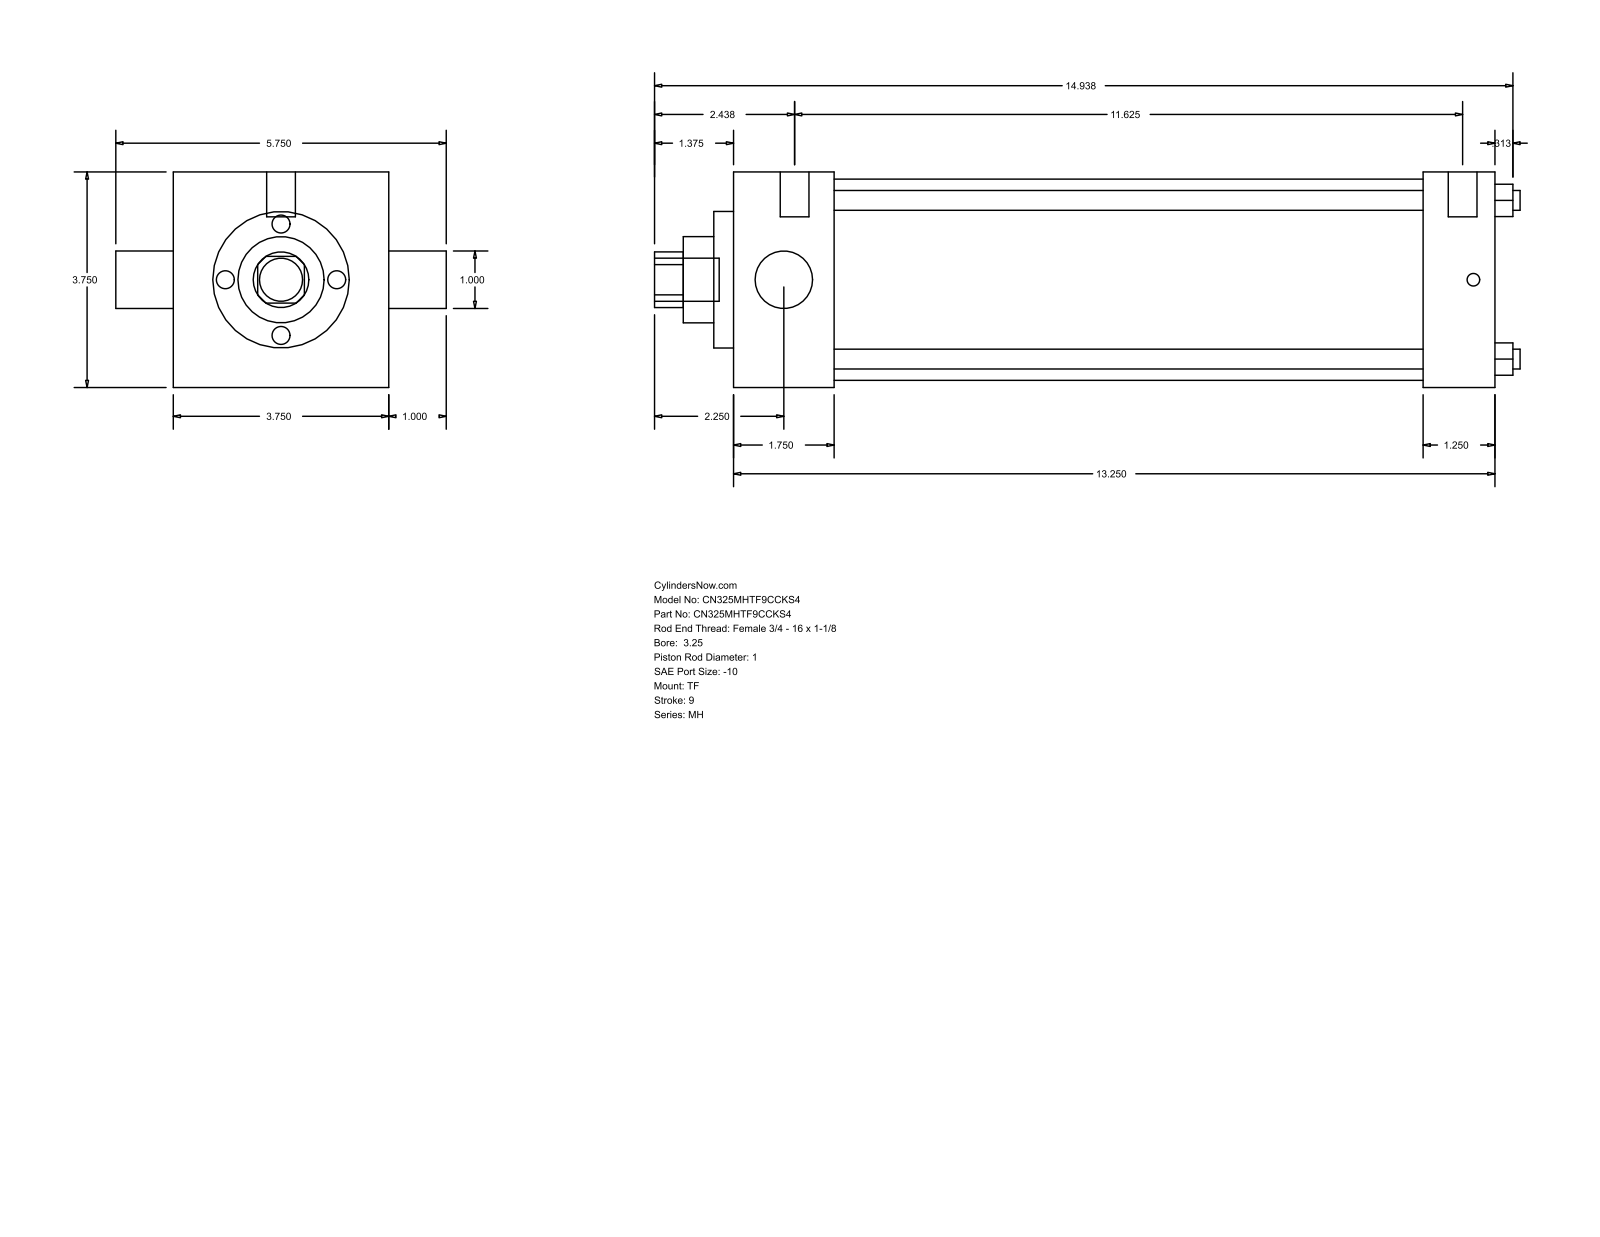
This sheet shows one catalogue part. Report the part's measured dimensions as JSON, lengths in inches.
{"part_name": "MH_TF__0325_1", "step_written_by": "GSSL Pune (CONFIG_CONTROL_DESIGN)", "units": "inches", "bodies": {"solids": 0, "faces": 86, "planar": 61, "cylindrical": 25, "other": 0}, "overall_size": [15.063, 5.75, 3.75], "round_holes": [[0.345, 4], [1, 2], [1.5, 1], [2.375, 1], [3.5, 1]], "round_bosses_or_shafts": [[0.219, 3], [0.5, 2], [0.75, 1]], "partial_cylinders_radius": [[0.484, 1]], "face_to_face_distances": [3.75, 13.25, 1.75, 12, 10.25, 11.5, 1.25, 0.344, 2.094, 12.344], "hole_center_spacings": [1.952, 2.76, 3.903]}
